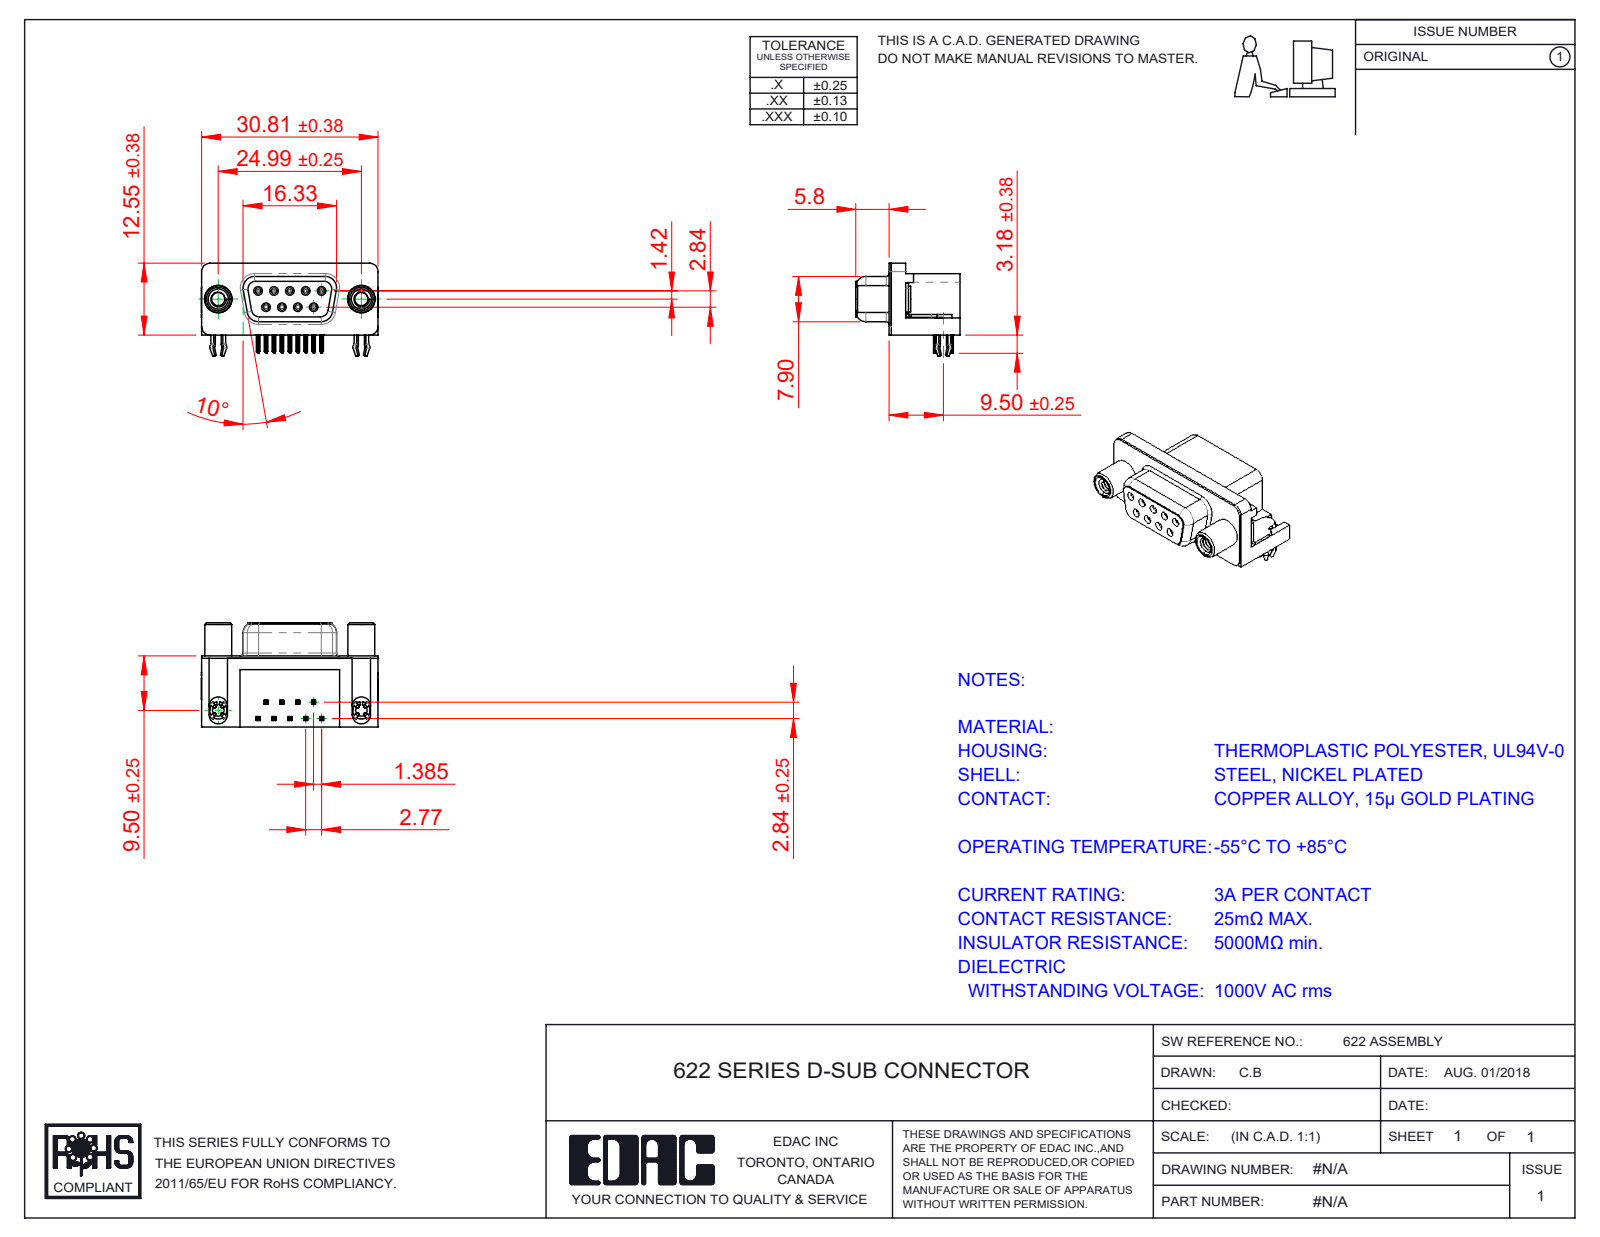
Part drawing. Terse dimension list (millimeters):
name: 622 Housing_9 Socket; 622-009-360-050; 622 Shell_9 Socket; 622 Round Threaded Standoff (+3 more)
written by: SolidWorks 2016 (CONFIG_CONTROL_DESIGN)
unit: mm
bodies: 15 solids, 1596 faces (676 planar, 436 cylindrical, 484 other)
size: 30.89 × 18.2 × 15.73
volume: 3 828 mm³; area: 5 352 mm²
holes: 9× ⌀0.8, 9× ⌀0.9, 2× ⌀2.26, 2× ⌀2.3, 2× ⌀3.1, 2× ⌀4, 2× ⌀4.8, 2× ⌀5
bosses: 9× ⌀1.2, 2× ⌀4.9, 2× ⌀4.7, 2× ⌀4.5, 2× ⌀3.85, 2× ⌀3.26
rounds: 72× R0.1, 36× R0.15, 18× R0.35, 18× R1, 9× R0.34, 8× R1.35, 8× R1.6, 7× R1.5
face distances: 0.4, 12, 12.4, 0.35, 2.9, 2.5, 10.34, 5.8, 9.5, 6.2
hole spacings: 3.16, 2.77, 5.54, 5.03, 5.04, 8.31, 7.48, 7.49
